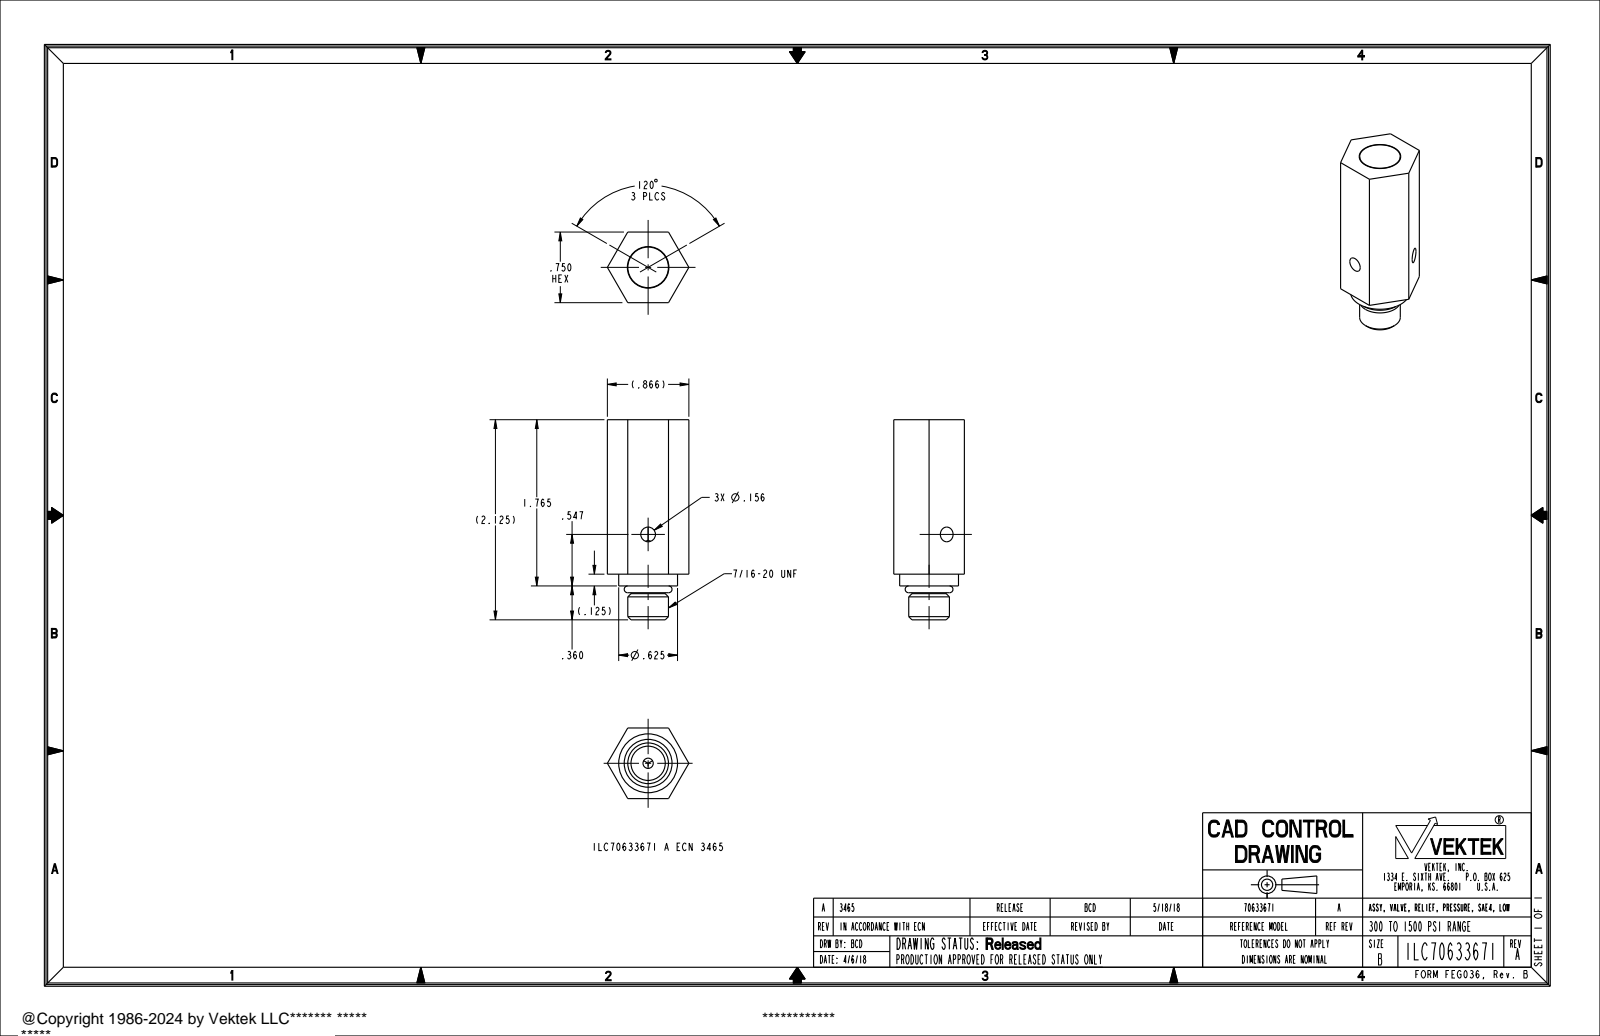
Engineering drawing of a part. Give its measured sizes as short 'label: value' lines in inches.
name: ILC70633671
written by: PRO/ENGINEER BY PARAMETRIC TECHNOLOGY CORPORATION, 2013320 (AUTOMOTIVE_DESIGN)
unit: in
bodies: 2 solids, 38 faces (12 planar, 18 cylindrical, 8 other)
size: 2.125 × 0.866 × 0.75
volume: 0.862 in³; area: 7.2 in²
holes: 3× ⌀0.156, 1× ⌀0.109, 1× ⌀0.441
bosses: 1× ⌀0.625, 1× ⌀0.432, 1× ⌀0.431, 1× ⌀0.364
face distances: 0.75, 1.765, 0.125, 1.64, 0.36, 0.485, 2.125, 2.055, 1.695, 1.57
